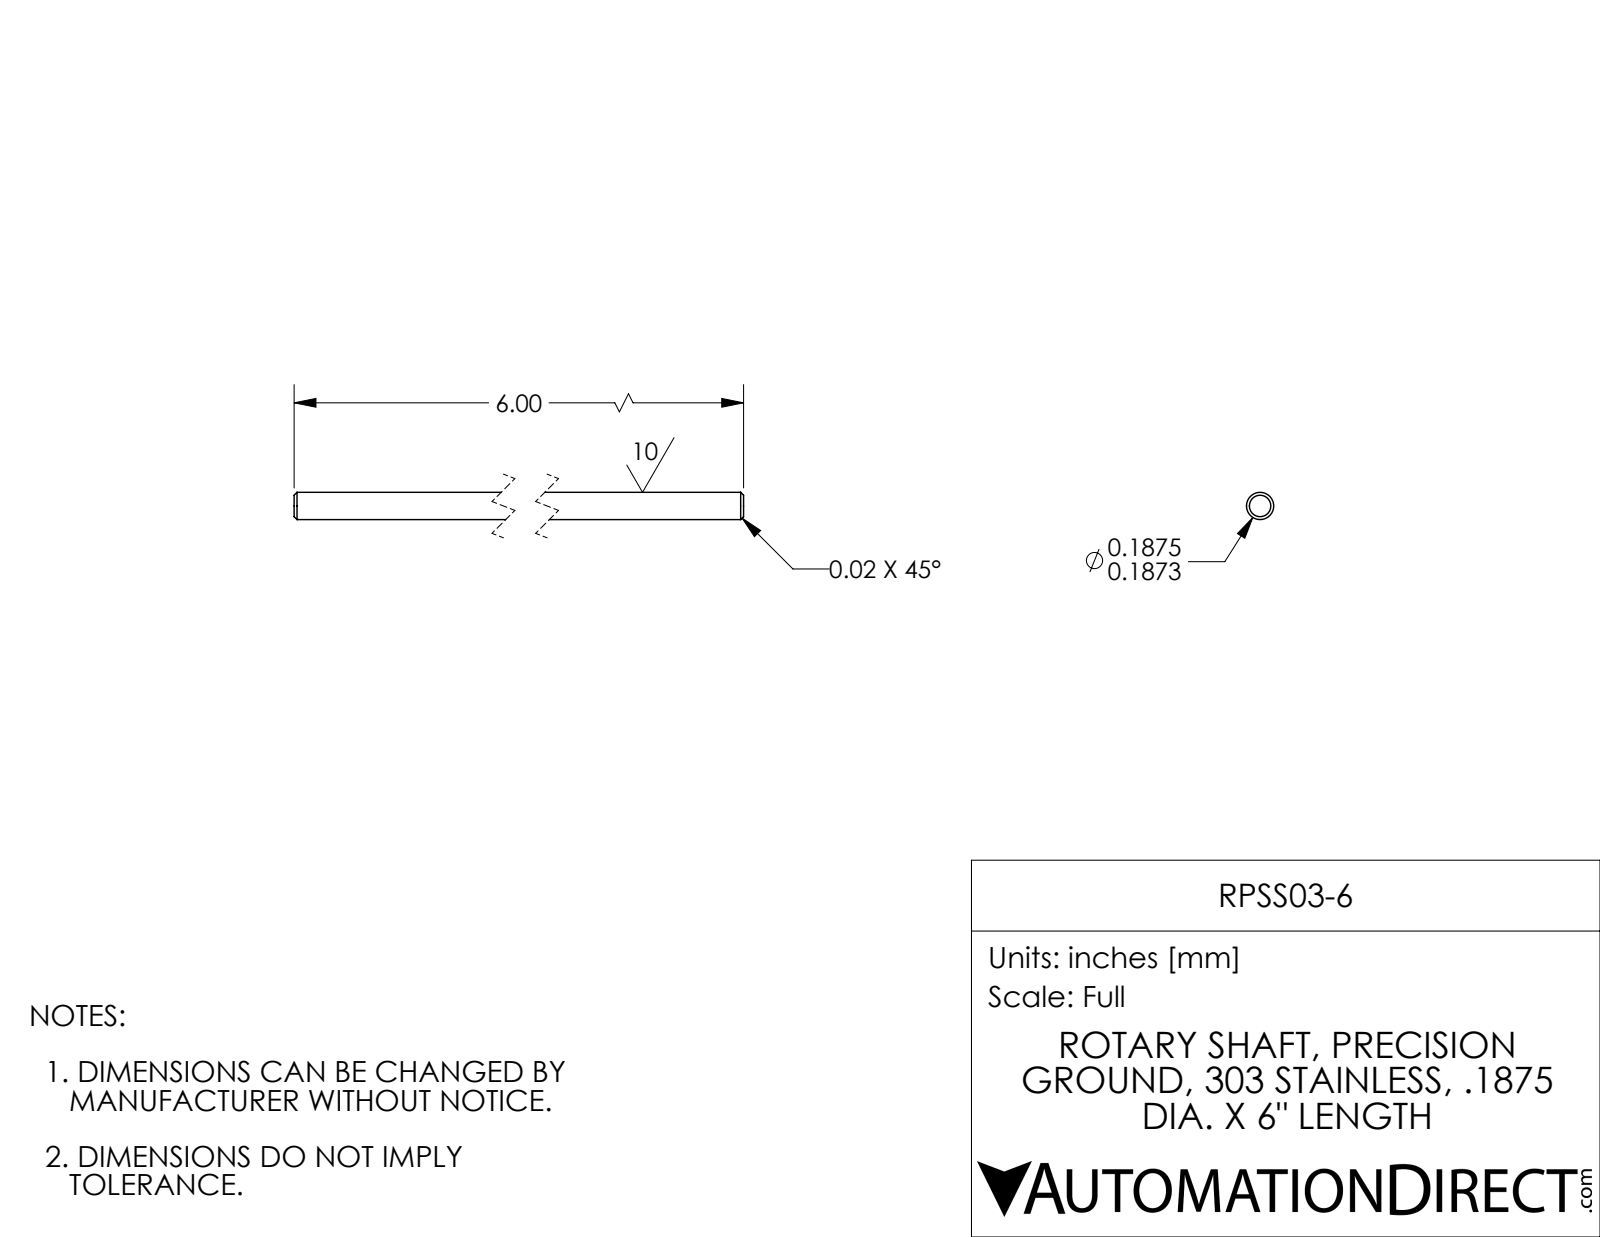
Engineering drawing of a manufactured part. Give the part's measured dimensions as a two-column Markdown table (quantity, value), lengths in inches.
| quantity | value |
| --- | --- |
| part name | RPSS03-6 |
| STEP written by | SolidWorks 2017 (AUTOMOTIVE_DESIGN) |
| units | inches |
| bodies | 1 solid, 8 faces (2 planar, 2 cylindrical, 4 other) |
| overall size | 6 × 0.188 × 0.188 |
| volume | 0.165 in³ |
| surface area | 3.575 in² |
| round bosses / shafts (diameter × count) | 0.187 × 1 |
| main face-to-face distances | 6 |
